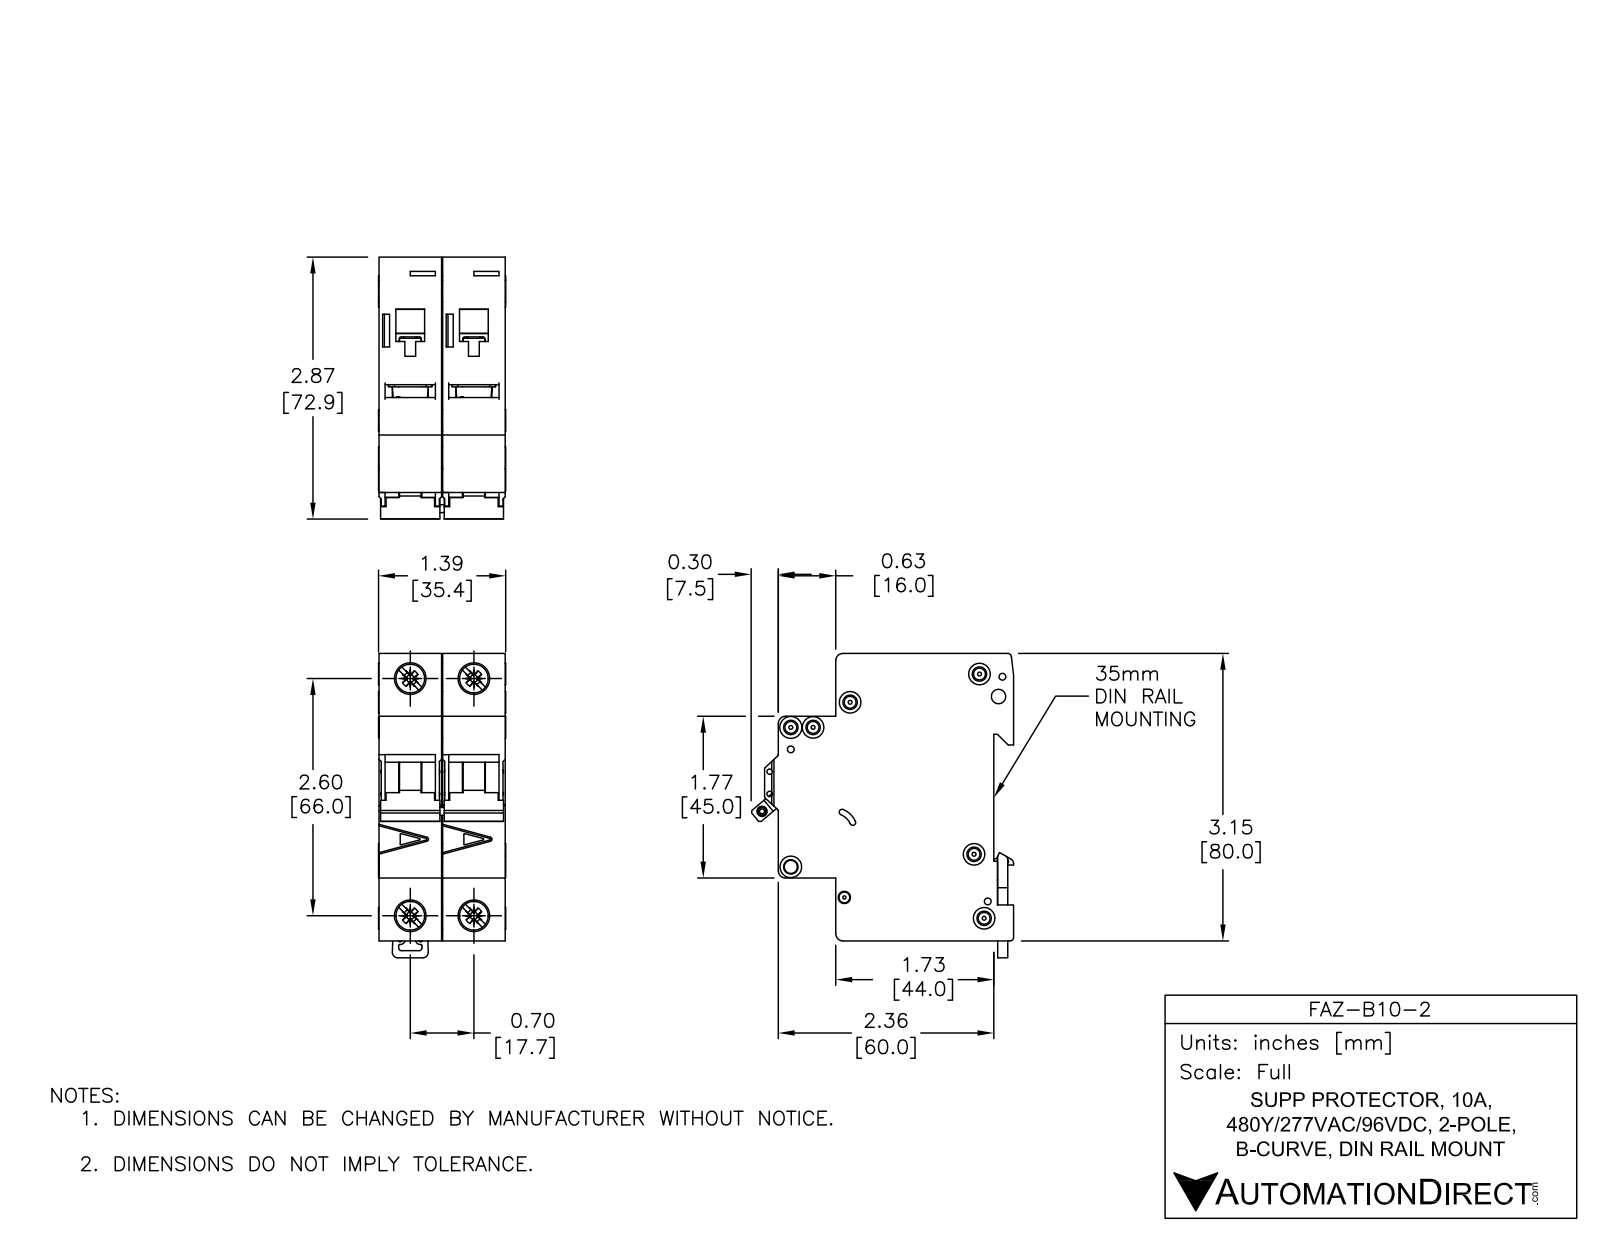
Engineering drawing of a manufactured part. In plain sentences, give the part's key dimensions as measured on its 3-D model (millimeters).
The part is named "FAZ-B10-2". Its 3-D file was written by "SolidWorks 2014 (AUTOMOTIVE_DESIGN)". It is 8 solids with 1104 faces: 466 planar, 396 cylindrical and 242 other. Overall it measures 84.78 by 73.04 by 35.4 millimeters. Its volume is 149 808 cubic millimeters and its surface area 38 799 square millimeters. Round holes: 6 of diameter 3.6, 3 of diameter 1.9, 2 of diameter 1.09, 2 of diameter 1.5, 2 of diameter 4, 2 of diameter 7.15, 2 of diameter 8.2, 1 of diameter 2.15, 1 of diameter 2.2, 1 of diameter 2.55, 1 of diameter 3.3, 1 of diameter 3.4. Round bosses or shafts: 4 of diameter 6, 2 of diameter 8.2, 2 of diameter 2.5. Partial cylindrical surfaces (rounded edges, fillets, slot ends): 49 of radius 0.25, 19 of radius 0.5, 10 of radius 2, 8 of radius 0.2, 8 of radius 1, 2 of radius 0.8, 2 of radius 1.8, 2 of radius 3. The main face-to-face distances are 17.7, 17.5, 35.2, 79.48, 5.5, 49.5, 44, 65.5, 60, 16. The hole center spacings are 6.2, 13.64, 17.7, 66, 68.33, 4.81, 5.19, 5.61.
